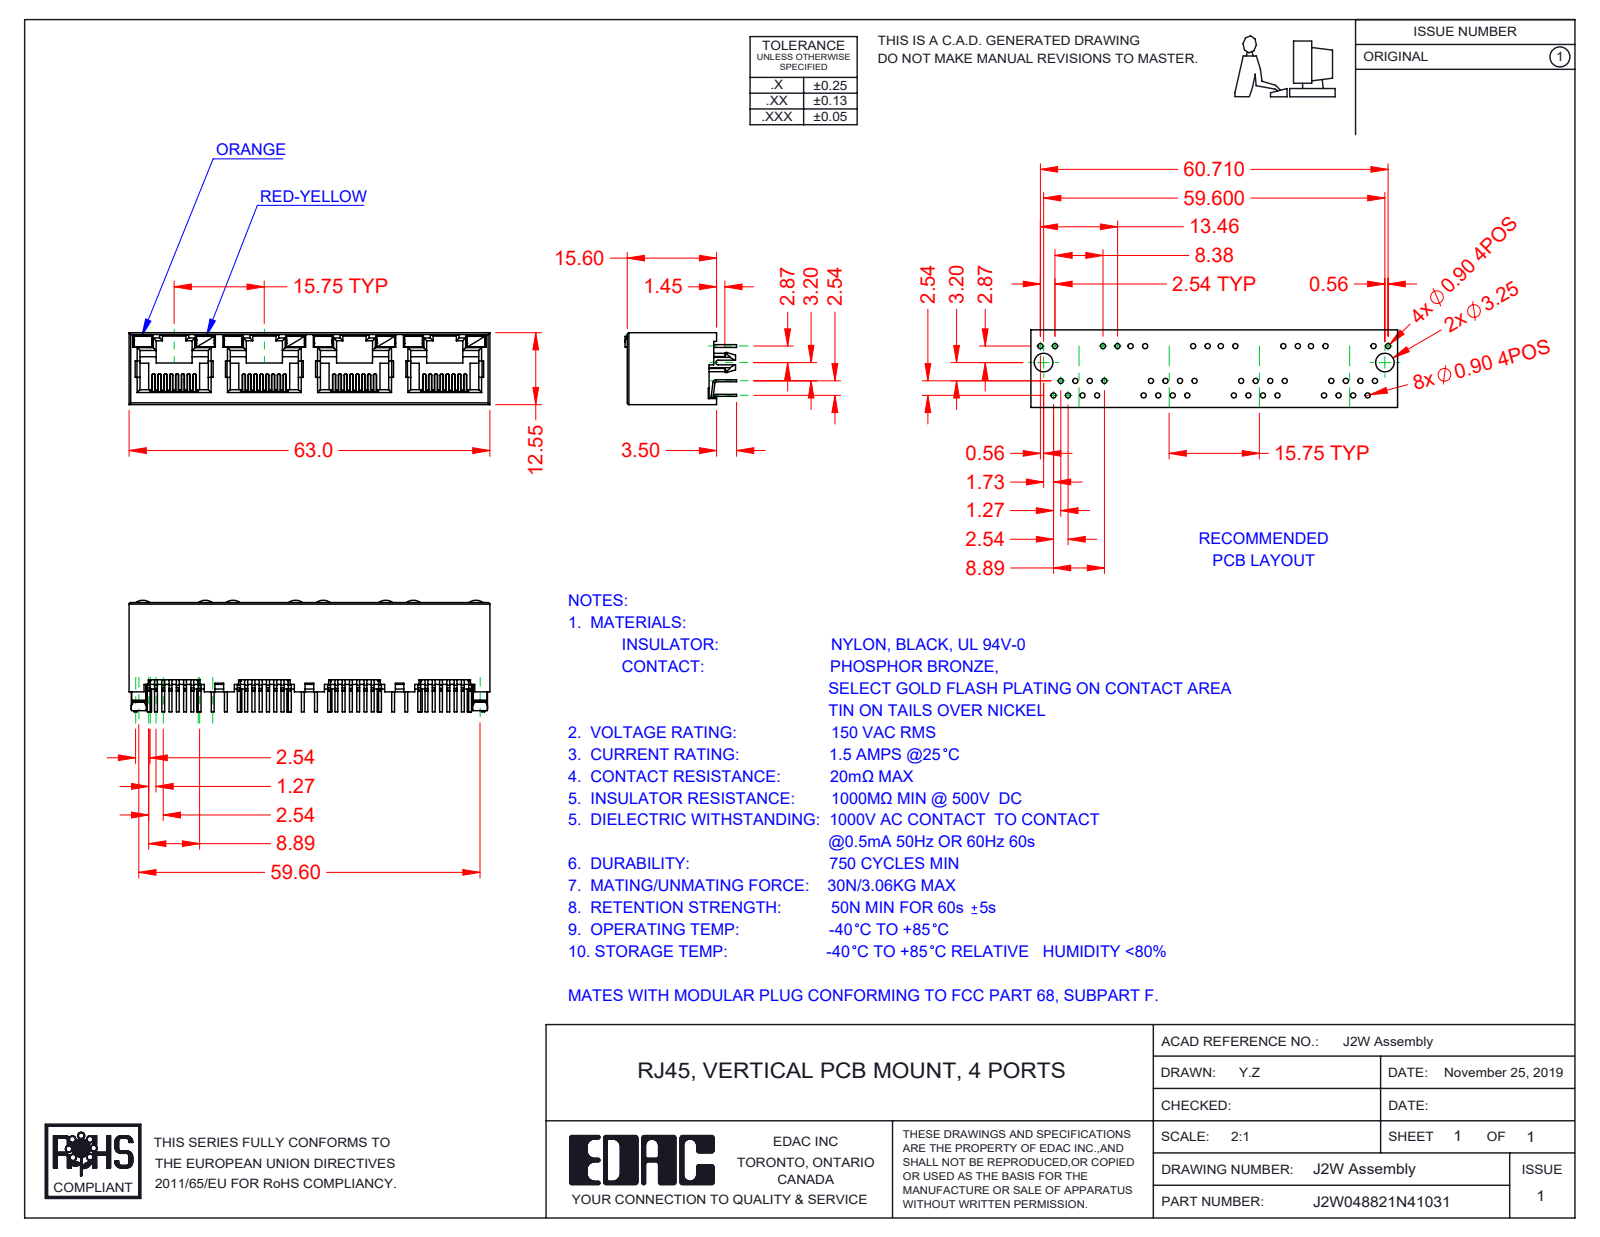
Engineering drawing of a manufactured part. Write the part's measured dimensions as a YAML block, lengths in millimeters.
part_name: "2W LED RH_8-Red-Yellow; 2W LED LH_4-Orange; J2W048821N48131; 2W Contact Lock (+2 more)"
step_written_by: "SolidWorks 2016 (CONFIG_CONTROL_DESIGN)"
units: millimeters
bodies: {solids: 45, faces: 3139, planar: 2600, cylindrical: 481, other: 58}
overall_size: [63, 19.5, 12.55]
volume: 5335
surface_area: 13144
partial_cylinders:
  - {radius: 0.15, count: 64}
  - {radius: 0.2, count: 29}
  - {radius: 0.5, count: 28}
  - {radius: 0.3, count: 14}
  - {radius: 0.45, count: 8}
  - {radius: 2, count: 8}
  - {radius: 0.25, count: 2}
  - {radius: 1.5, count: 2}
face_to_face_distances: [12.55, 11.9, 0.65, 15.75, 0.36, 1.5, 0.78, 0.6, 11.3, 31.5]
